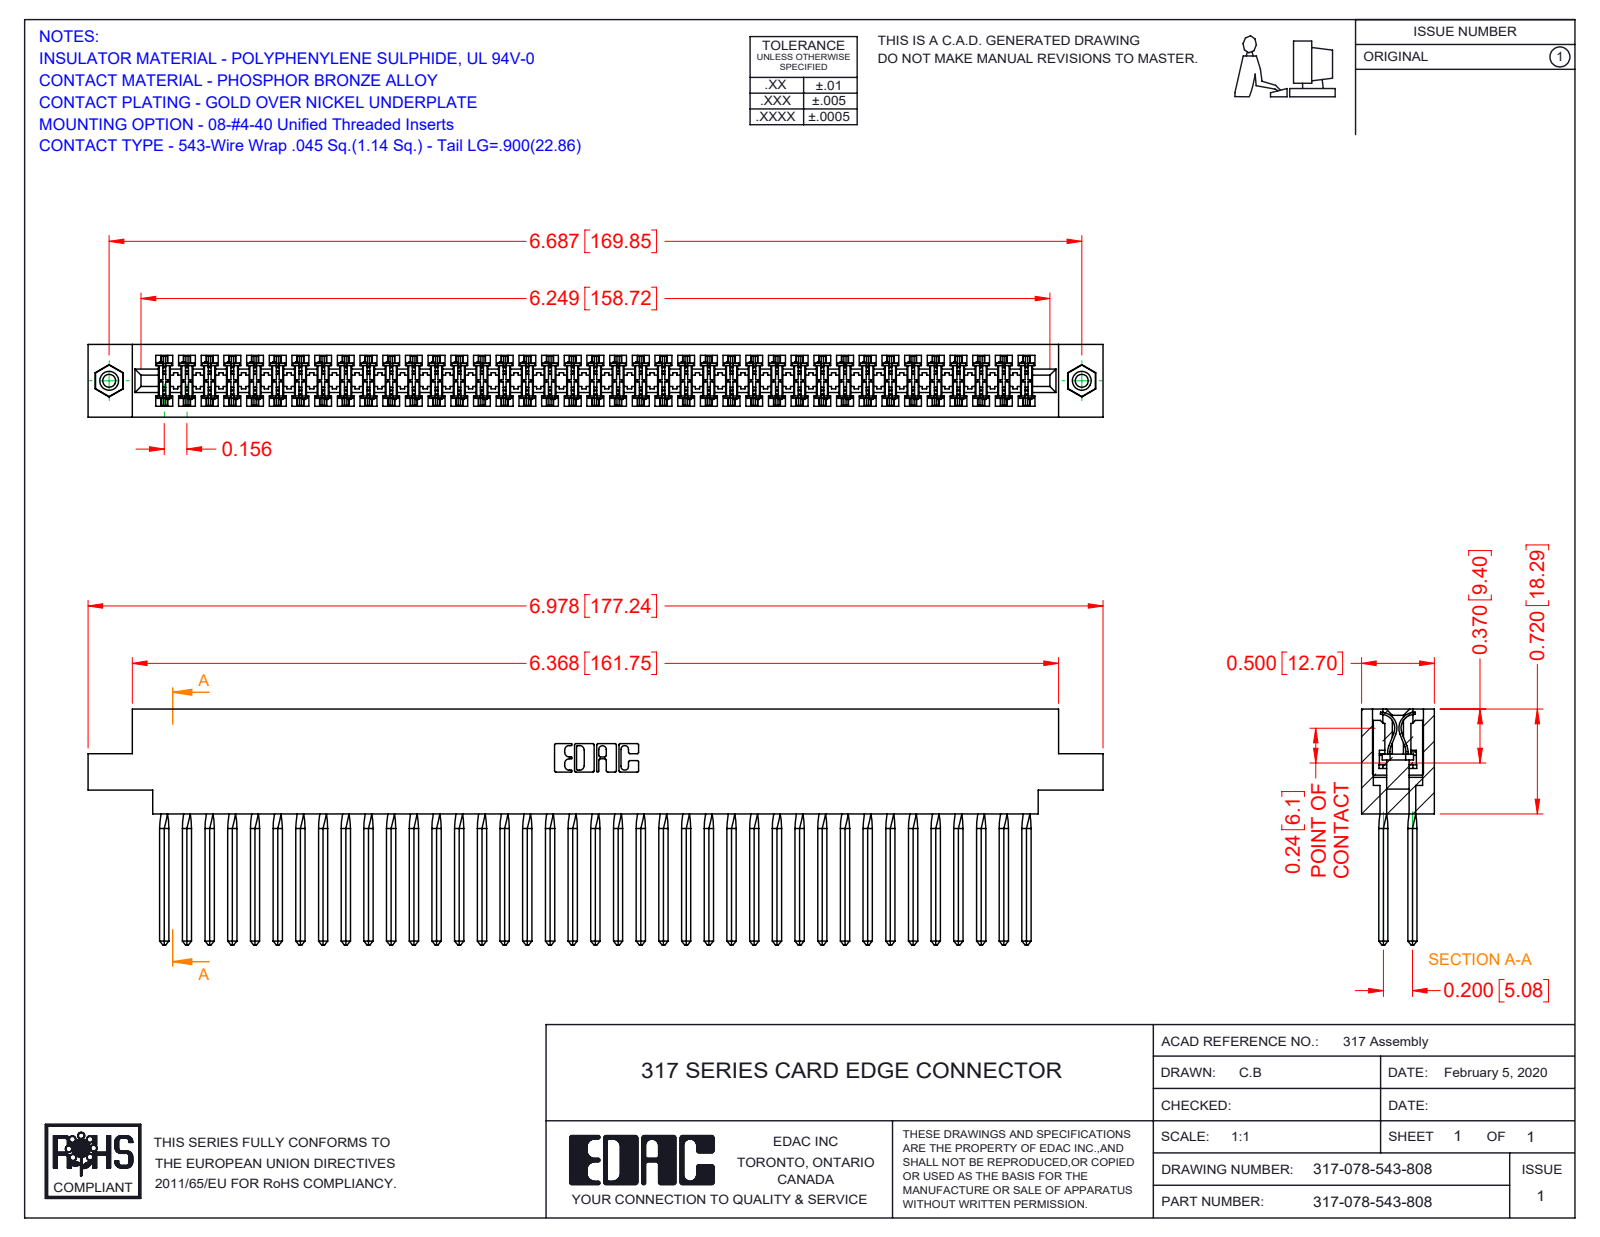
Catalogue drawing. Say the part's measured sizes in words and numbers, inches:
The part is named "317-078-543-878; 317-290-001_543; 317 Part_.156 Dia - TI; 345-250-001_345-250-003-102". Its 3-D file was written by "SolidWorks 2016 (CONFIG_CONTROL_DESIGN)". It is 81 solids with 7104 faces: 5784 planar, 992 cylindrical and 328 other. Overall it measures 6.978 by 1.62 by 0.5 inches. Its volume is 1.832 cubic inches and its surface area 70.46 square inches. Round holes: 2 of diameter 0.089, 2 of diameter 0.125, 2 of diameter 0.156. Round bosses or shafts: 2 of diameter 0.155. Partial cylindrical surfaces (rounded edges, fillets, slot ends): 156 of radius 0.015, 22 of radius 0.01, 6 of radius 0.007, 6 of radius 0.031, 3 of radius 0.026, 2 of radius 0.095, 2 of radius 0.1, 2 of radius 0.11. The main face-to-face distances are 0.5, 0.075, 0.425, 0.35, 0.11, 0.195, 0.094, 0.2, 0.115, 0.131. The hole center spacings are 6.687.
